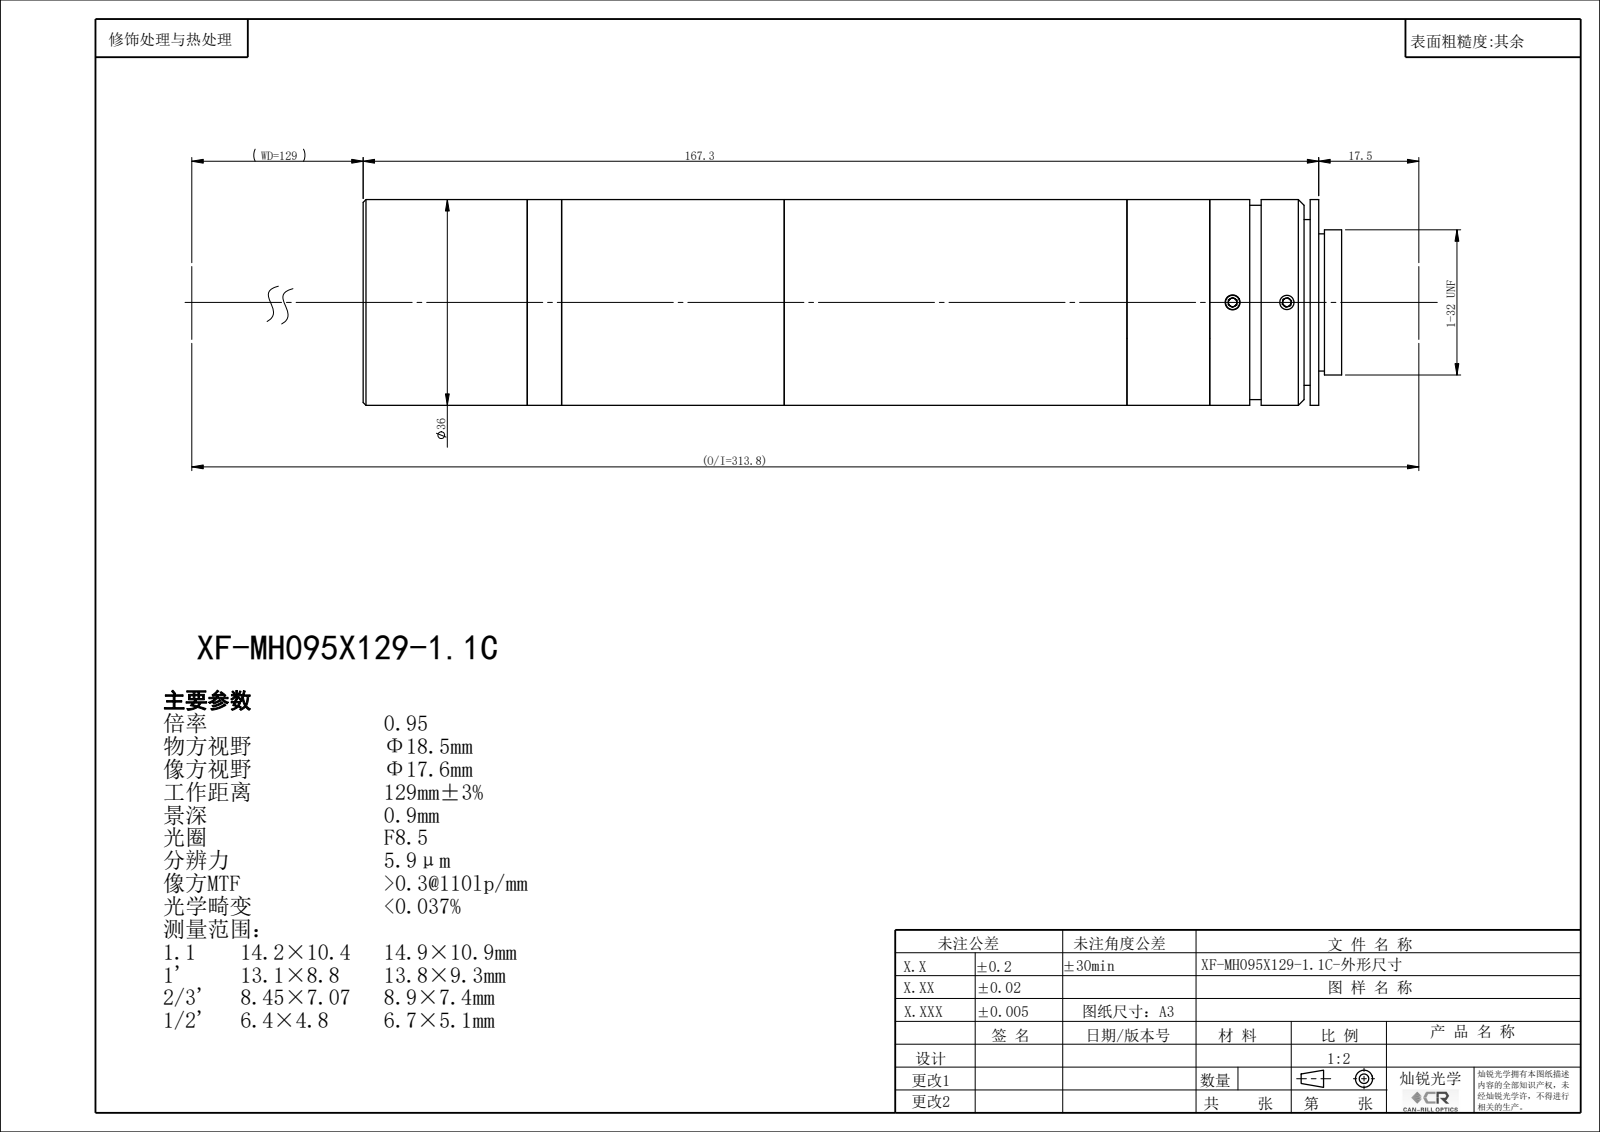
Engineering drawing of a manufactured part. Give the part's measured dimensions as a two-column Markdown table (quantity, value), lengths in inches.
| quantity | value |
| --- | --- |
| part name | XF-MH095X129-1.1C |
| STEP written by | SolidWorks 2022 (CONFIG_CONTROL_DESIGN) |
| units | inches |
| bodies | 0 solids, 132 faces (68 planar, 42 cylindrical, 22 other) |
| overall size | 6.744 × 1.417 × 1.417 |
| round holes (diameter × count) | 0.098 × 3, 0.882 × 1, 0.945 × 1, 1.024 × 1, 1.039 × 1, 1.157 × 1, 1.315 × 1, 1.358 × 1 |
| round bosses / shafts (diameter × count) | 1.417 × 1, 1.339 × 1, 1 × 1 |
| main face-to-face distances | 0.751, 0.059, 0.692, 0.571, 1.263, 1.322, 2.362, 2.933, 3.625, 3.684 |
